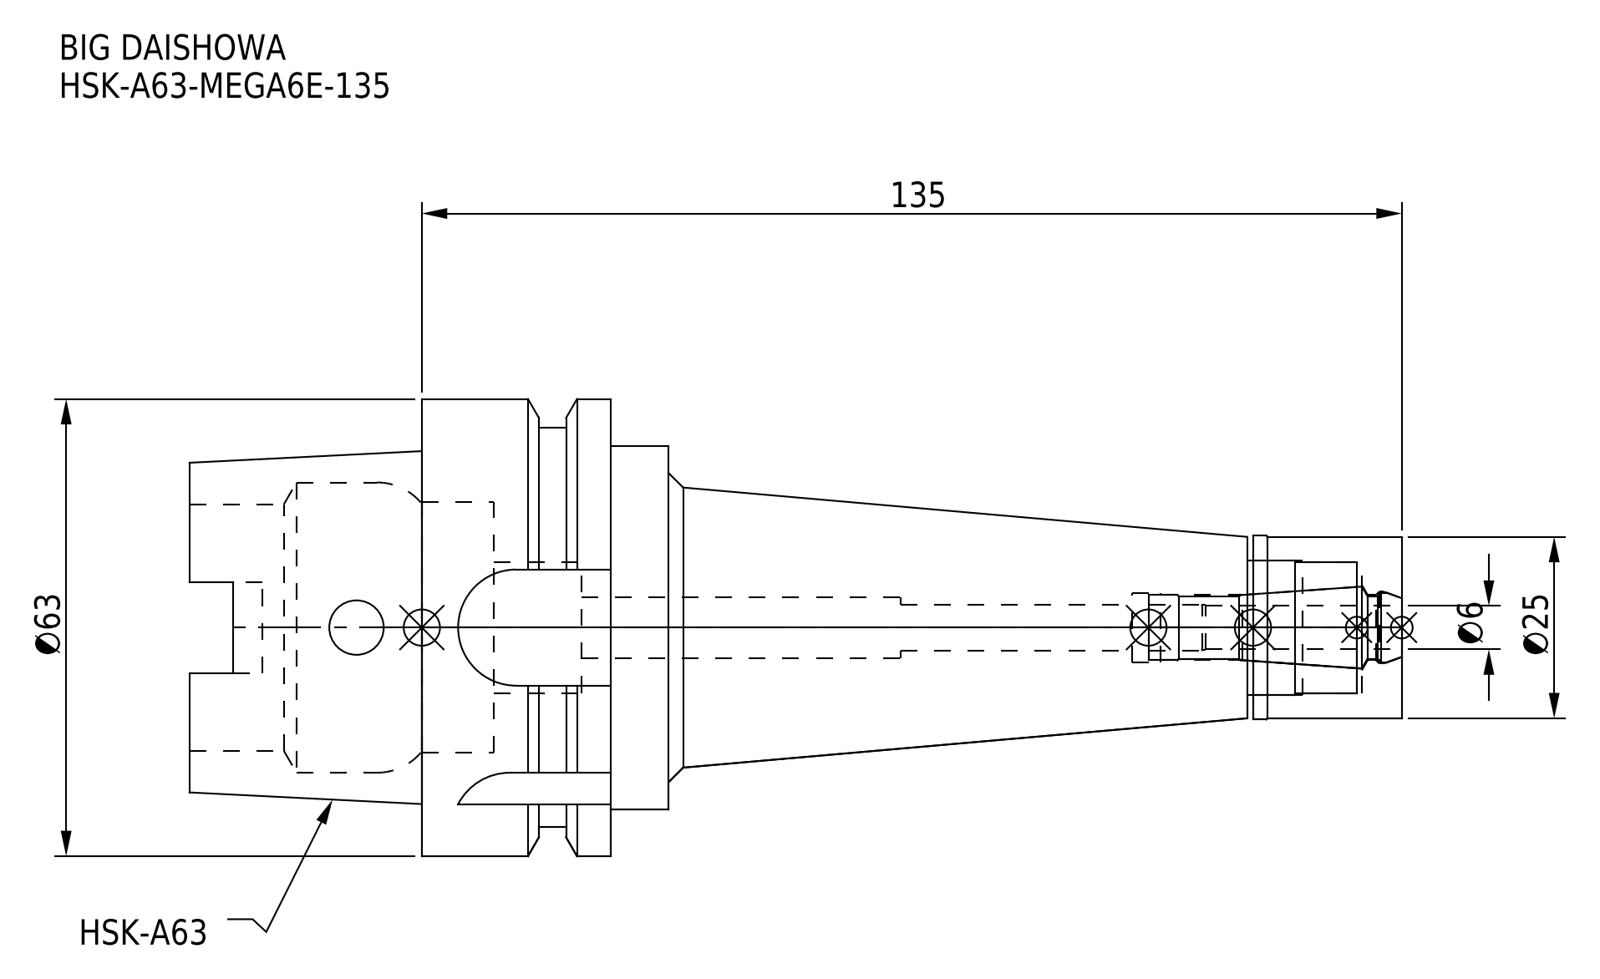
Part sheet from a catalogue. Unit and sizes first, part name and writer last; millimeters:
Units: millimetres
Overall size (bounding box): 167 × 63 × 63
Round holes (diameter × count): ⌀6.4 ×1, ⌀7.5 ×1, ⌀8.4 ×1, ⌀9 ×1, ⌀9.6 ×1, ⌀9.9 ×1, ⌀18 ×1, ⌀18.5 ×1, ⌀34 ×1, ⌀34.5 ×1, ⌀40 ×1
Round bosses / shafts (diameter × count): ⌀63 ×1, ⌀55 ×1, ⌀50 ×1, ⌀25.3 ×1, ⌀25 ×1
Partial cylindrical surfaces — rounded edges, fillets, slot ends (radius × count): R2.8 ×2, R2.88 ×2, R8 ×2, R9 ×1
Main face-to-face distances: 26, 16.05, 9.95, 8, 24.05, 34, 101, 109, 125.05, 135
Volume: 166 820 mm³ · Surface area: 37 825 mm²
Bodies: 2 solids, 127 faces (45 planar, 54 cylindrical, 28 other)
Part name (STEP PRODUCT): HA63ME06135-060_ASM.stp; HSK-A63-MEGA6E-135_1.stp; MEN6_1.stp; DXF_TEMP_ASSY_ASM_4_ASM.stp (+3 more)
STEP written by: SolidWorks 2019 (CONFIG_CONTROL_DESIGN)
